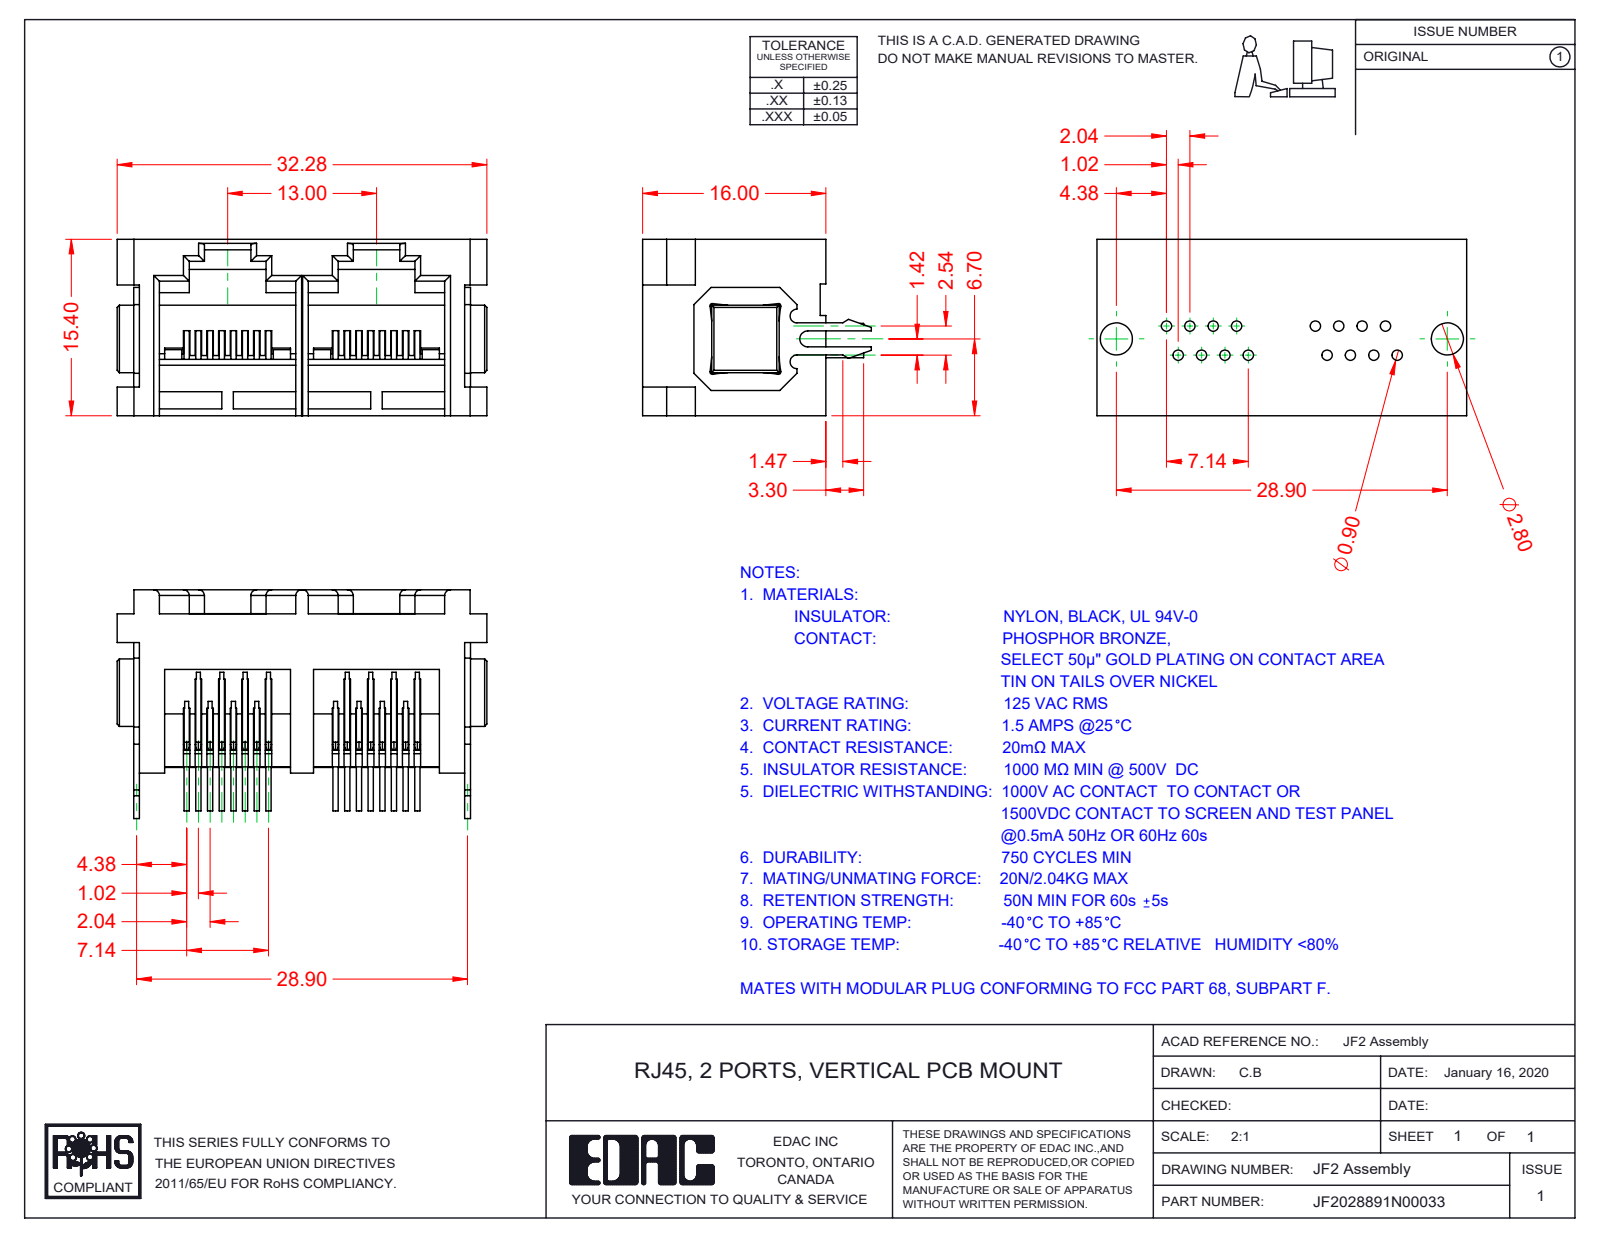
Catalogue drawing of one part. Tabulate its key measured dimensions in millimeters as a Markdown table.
| quantity | value |
| --- | --- |
| part name | F2 Contact Lock; F2 Contacts; F2 Insulator; RJF2028891N00033 (+1 more) |
| STEP written by | SolidWorks 2016 (CONFIG_CONTROL_DESIGN) |
| units | millimeters |
| bodies | 21 solids, 1130 faces (734 planar, 300 cylindrical, 96 other) |
| overall size | 32.28 × 19.97 × 15.4 |
| volume | 3 519 mm³ |
| surface area | 6 910 mm² |
| round bosses / shafts (diameter × count) | 0.46 × 64 |
| partial cylindrical surfaces (radius × count) | 0.18 × 32, 0.5 × 15, 0.2 × 4, 20.35 × 4, 0.3 × 3, 0.6 × 2, 0.21 × 1, 0.45 × 1 |
| main face-to-face distances | 12.59, 2.1, 13, 1.5, 2.81, 0.92, 11.67, 0.5, 28.4, 11 |
